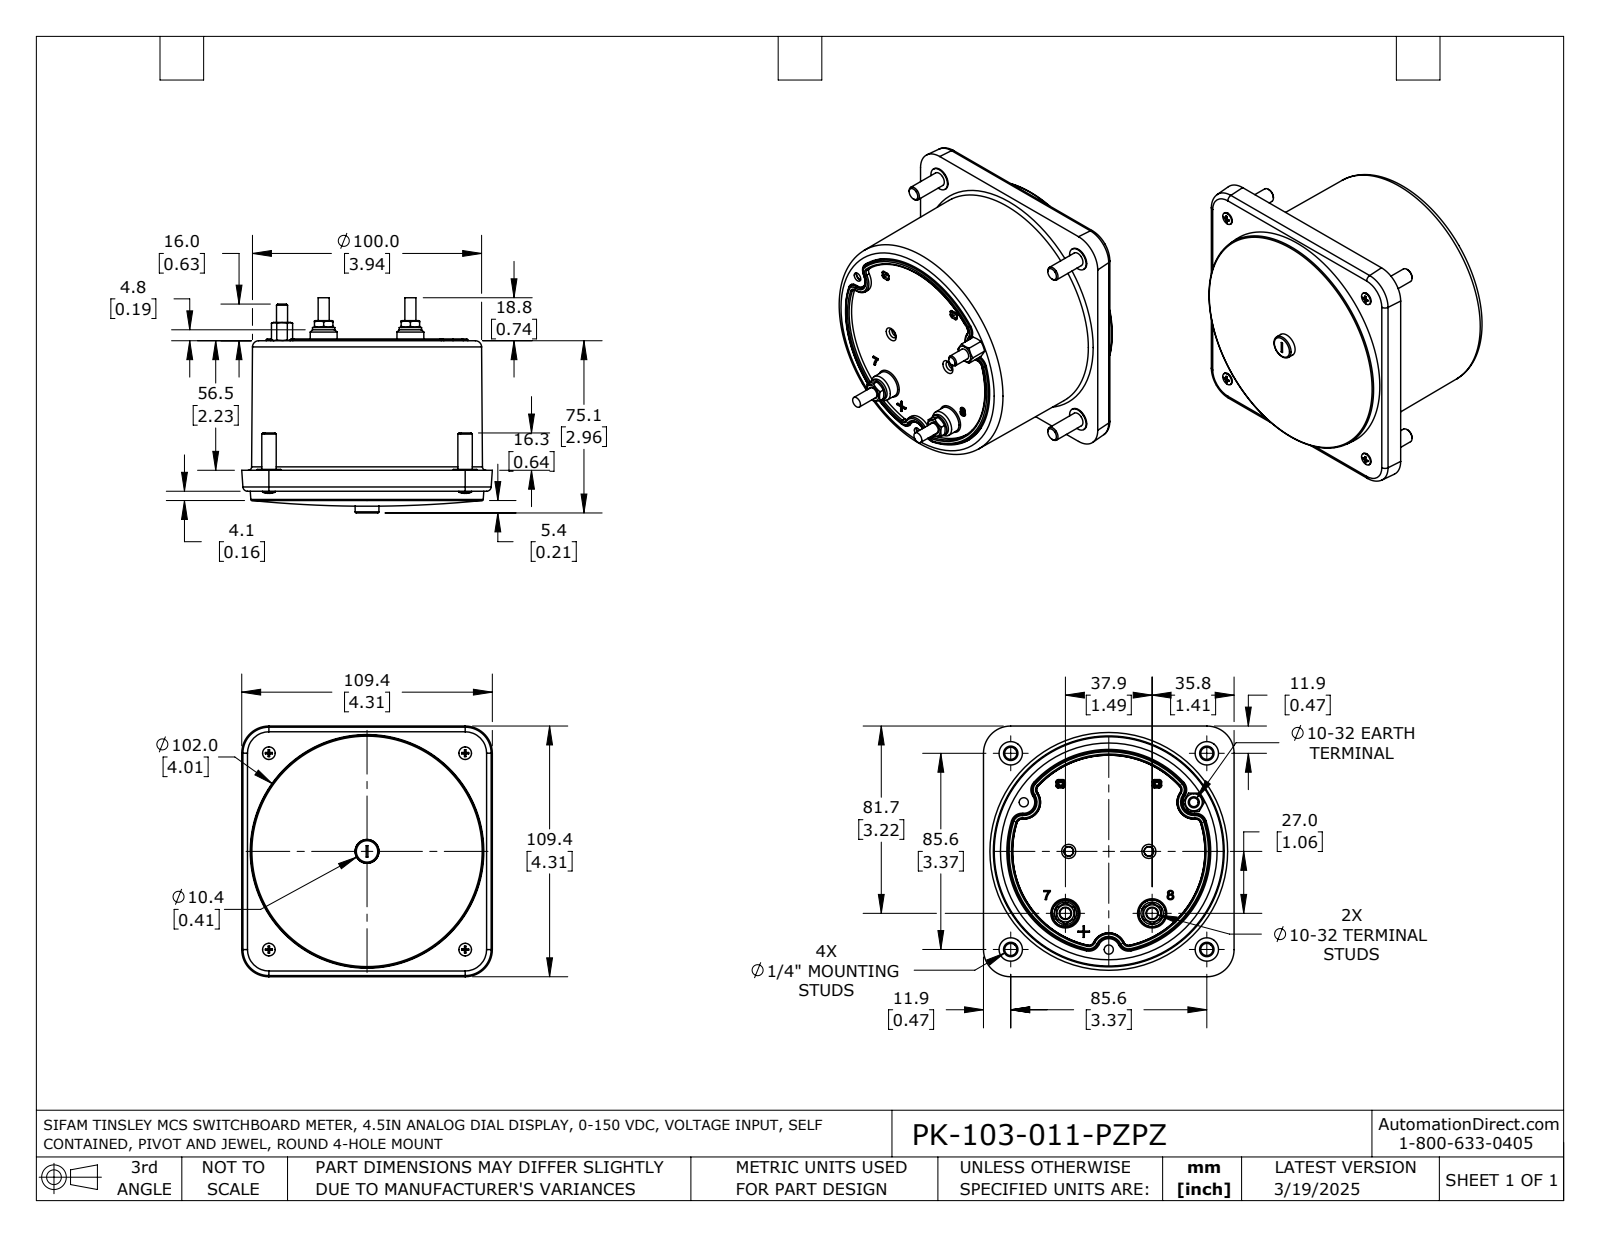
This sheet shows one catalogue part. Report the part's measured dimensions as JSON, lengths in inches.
{"part_name": "PK-103-011-PZPZ", "step_written_by": "SolidWorks 2021 (AUTOMOTIVE_DESIGN)", "units": "inches", "bodies": {"solids": 1, "faces": 609, "planar": 167, "cylindrical": 141, "other": 301}, "overall_size": [4.307, 4.307, 3.697], "volume_in3": 36.28, "surface_area_in2": 82.21, "round_holes": [[0.094, 4], [0.138, 4], [0.315, 4], [0.157, 3], [0.209, 2]], "round_bosses_or_shafts": [[0.402, 4], [0.248, 4], [0.217, 4], [0.114, 4], [0.19, 3], [0.384, 2], [0.146, 1]], "partial_cylinders_radius": [[0.02, 24], [0.189, 9], [0.079, 4], [1.752, 1]], "face_to_face_distances": [2.177, 2.537, 0.36, 0.048, 2.225, 2.585, 0.489, 2.715, 2.667, 0.129], "hole_center_spacings": [3.372, 3.37, 3.374, 3.378, 3.38, 4.769, 0.971, 1.126]}
